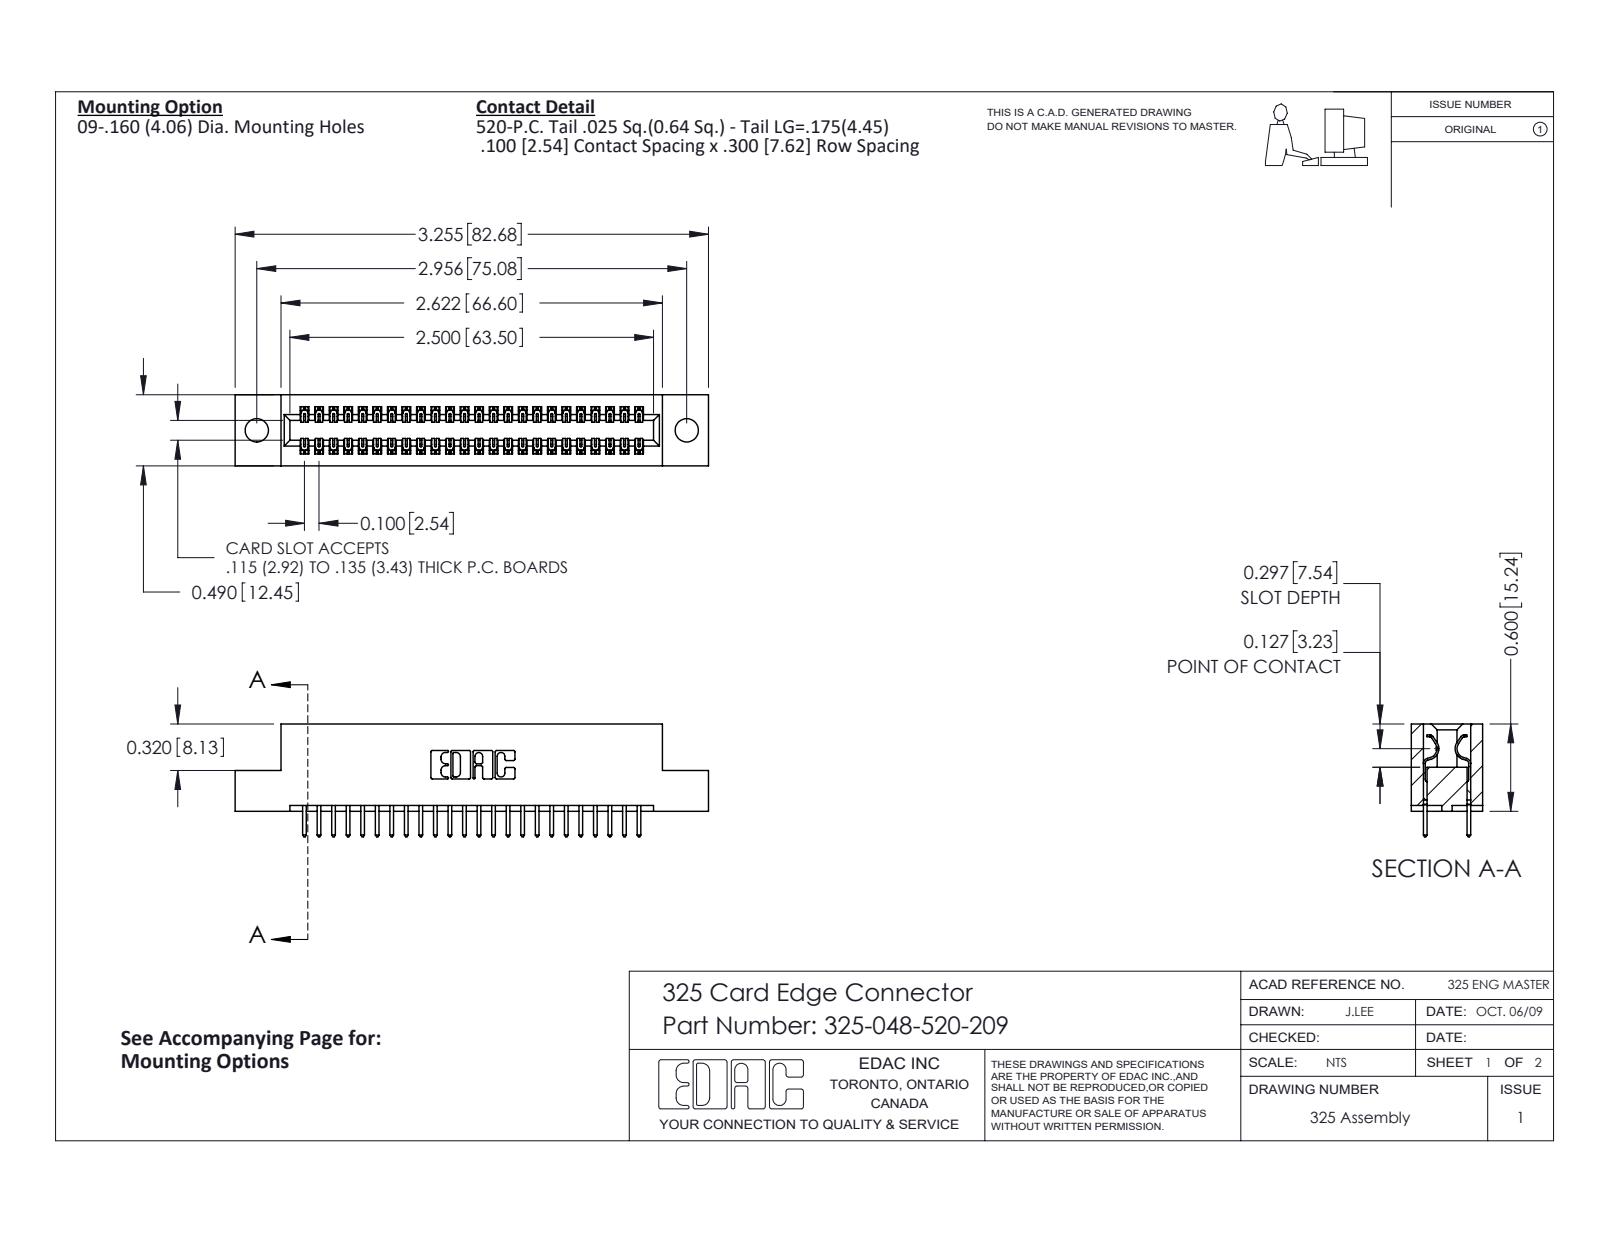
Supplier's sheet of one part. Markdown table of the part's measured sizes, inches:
| quantity | value |
| --- | --- |
| part name | 325-292-001_325-293-120; 325-048-520-209; 325 Part_.160 TH |
| STEP written by | SolidWorks 2016 (CONFIG_CONTROL_DESIGN) |
| units | inches |
| bodies | 49 solids, 2610 faces (1798 planar, 812 cylindrical, 0 other) |
| overall size | 3.255 × 0.775 × 0.49 |
| volume | 0.627 in³ |
| surface area | 18.34 in² |
| round holes (diameter × count) | 0.16 × 2 |
| partial cylindrical surfaces (radius × count) | 0.006 × 72, 0.01 × 48, 0.01 × 22, 0.007 × 6, 0.031 × 6, 0.026 × 3, 0.014 × 2, 0.022 × 2 |
| main face-to-face distances | 0.083, 0.407, 0.3, 0.49, 0.107, 0.383, 0.025, 0.325, 0.04, 0.6 |
| hole center spacings | 2.956 |
